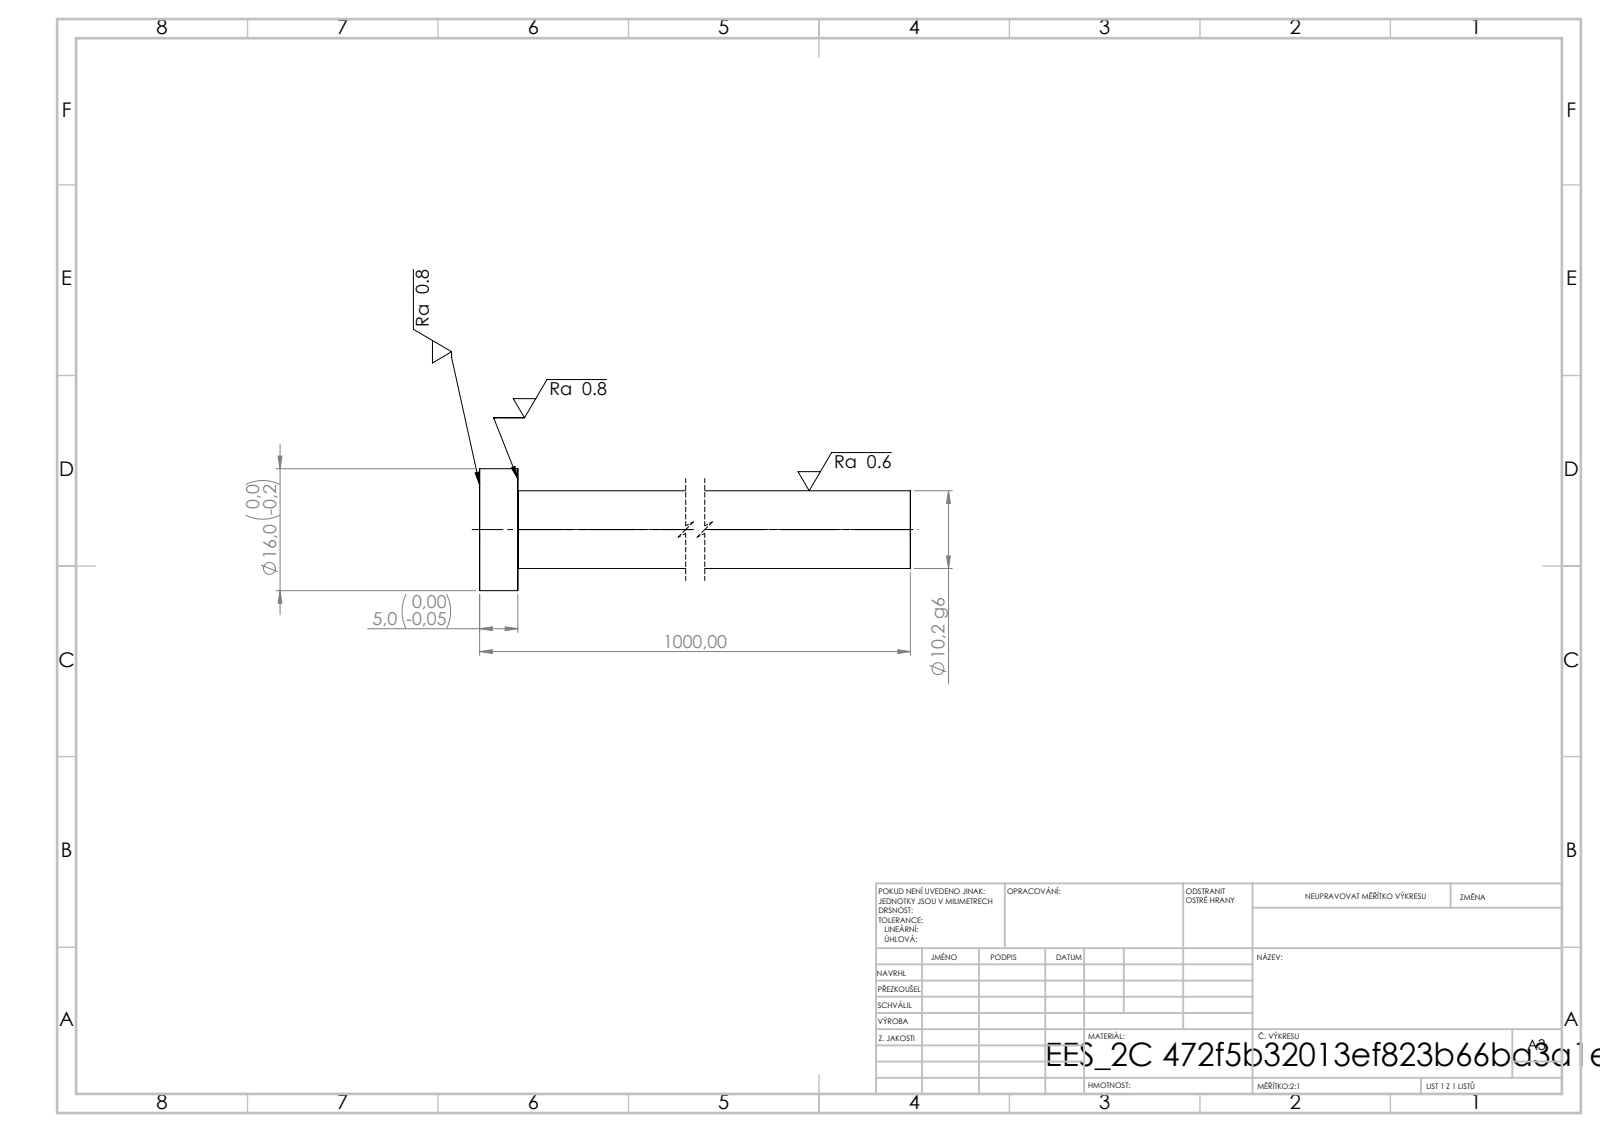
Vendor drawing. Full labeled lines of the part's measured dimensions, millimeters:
STEP written by: SolidWorks 2019 (CONFIG_CONTROL_DESIGN)
Units: millimetres
Bodies: 1 solid, 7 faces (3 planar, 4 cylindrical, 0 other)
Overall size (bounding box): 1000 × 16 × 16
Volume: 82 310 mm³ · Surface area: 32 537 mm²
Round bosses / shafts (diameter × count): ⌀16 ×1, ⌀10.2 ×1
Main face-to-face distances: 5, 1000, 995
